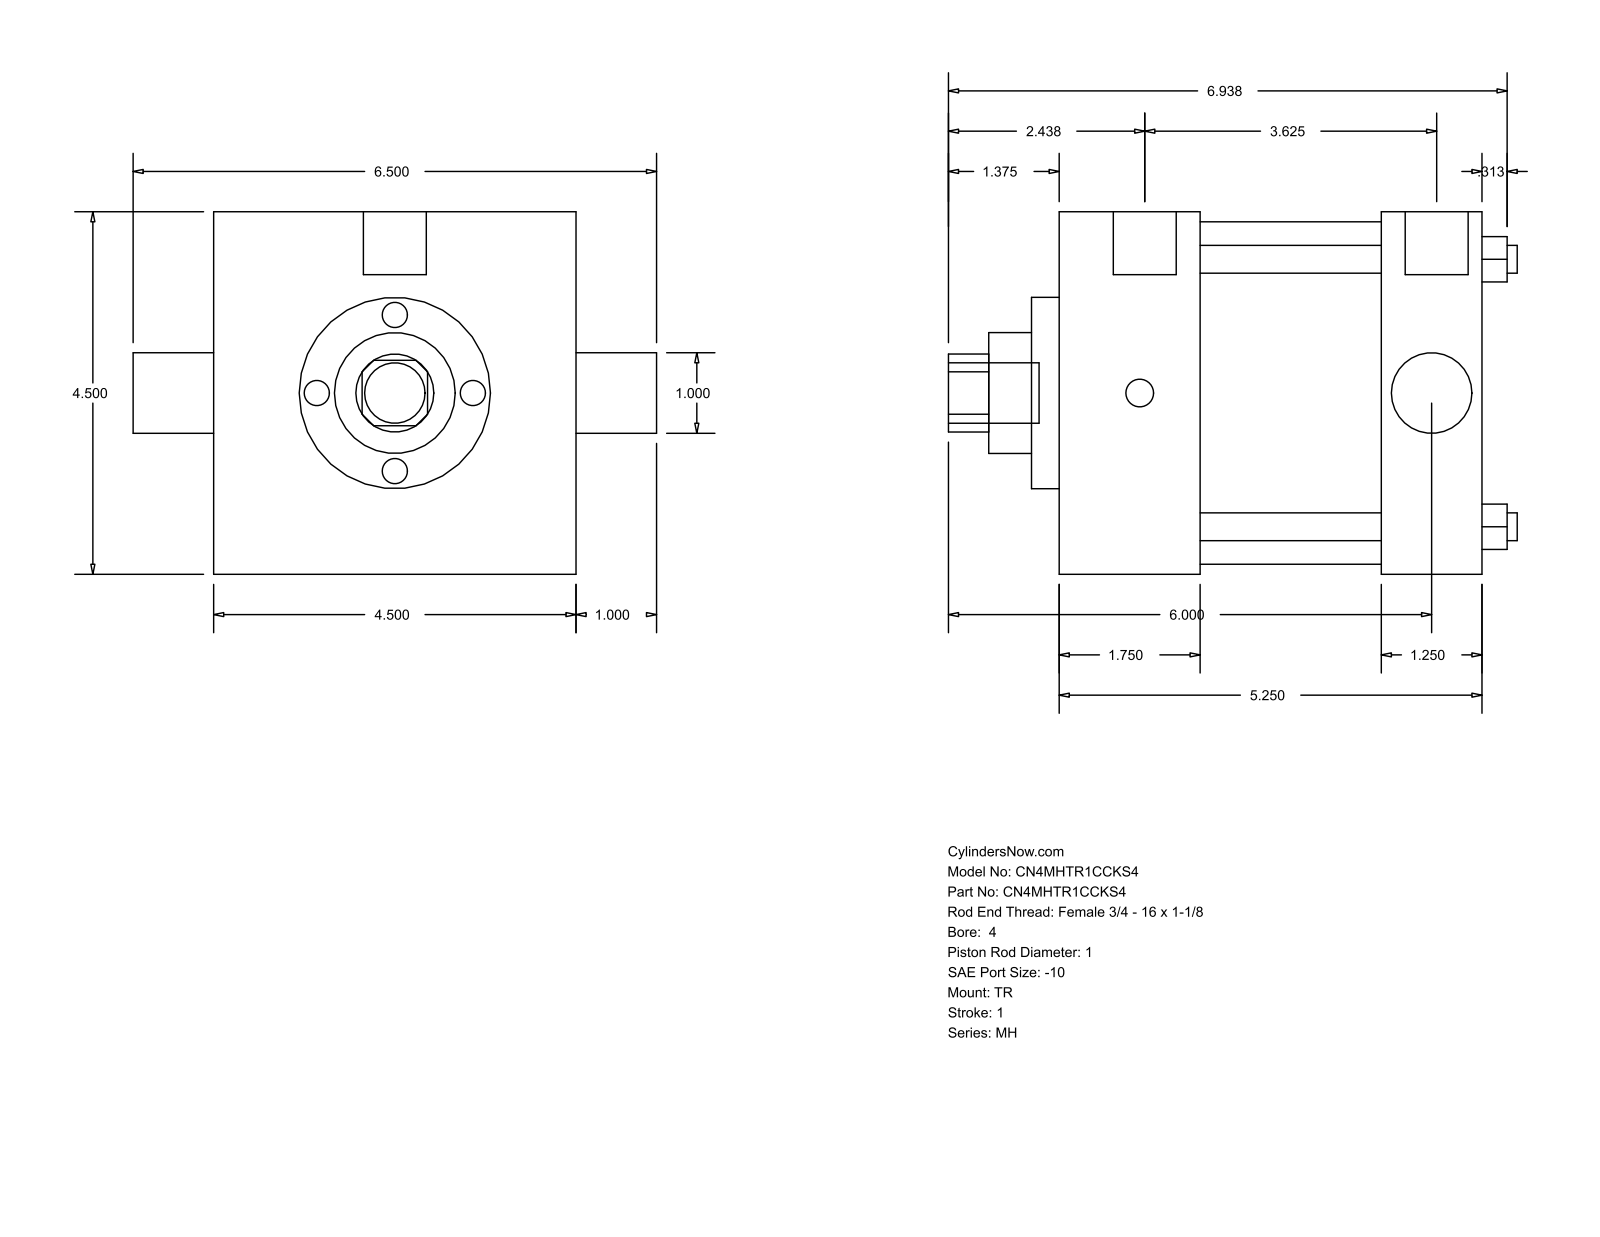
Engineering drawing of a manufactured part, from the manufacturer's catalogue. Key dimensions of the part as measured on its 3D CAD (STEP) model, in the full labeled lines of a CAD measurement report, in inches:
Part name (STEP PRODUCT): MH_TR__0400_1
STEP written by: GSSL Pune (CONFIG_CONTROL_DESIGN)
Units: inches
Bodies: 0 solids, 86 faces (61 planar, 25 cylindrical, 0 other)
Overall size (bounding box): 7.063 × 6.5 × 4.5
Round holes (diameter × count): ⌀0.345 ×4, ⌀1 ×2, ⌀1.5 ×1, ⌀2.375 ×1, ⌀4.25 ×1
Round bosses / shafts (diameter × count): ⌀0.344 ×3, ⌀0.781 ×2, ⌀0.75 ×1
Partial cylindrical surfaces — rounded edges, fillets, slot ends (radius × count): R0.484 ×1
Main face-to-face distances: 4.5, 5.25, 1.75, 3.5, 4, 2.25, 1.25, 0.344, 2.094, 4.344
Hole centre spacings: 2.347, 3.32, 4.695
